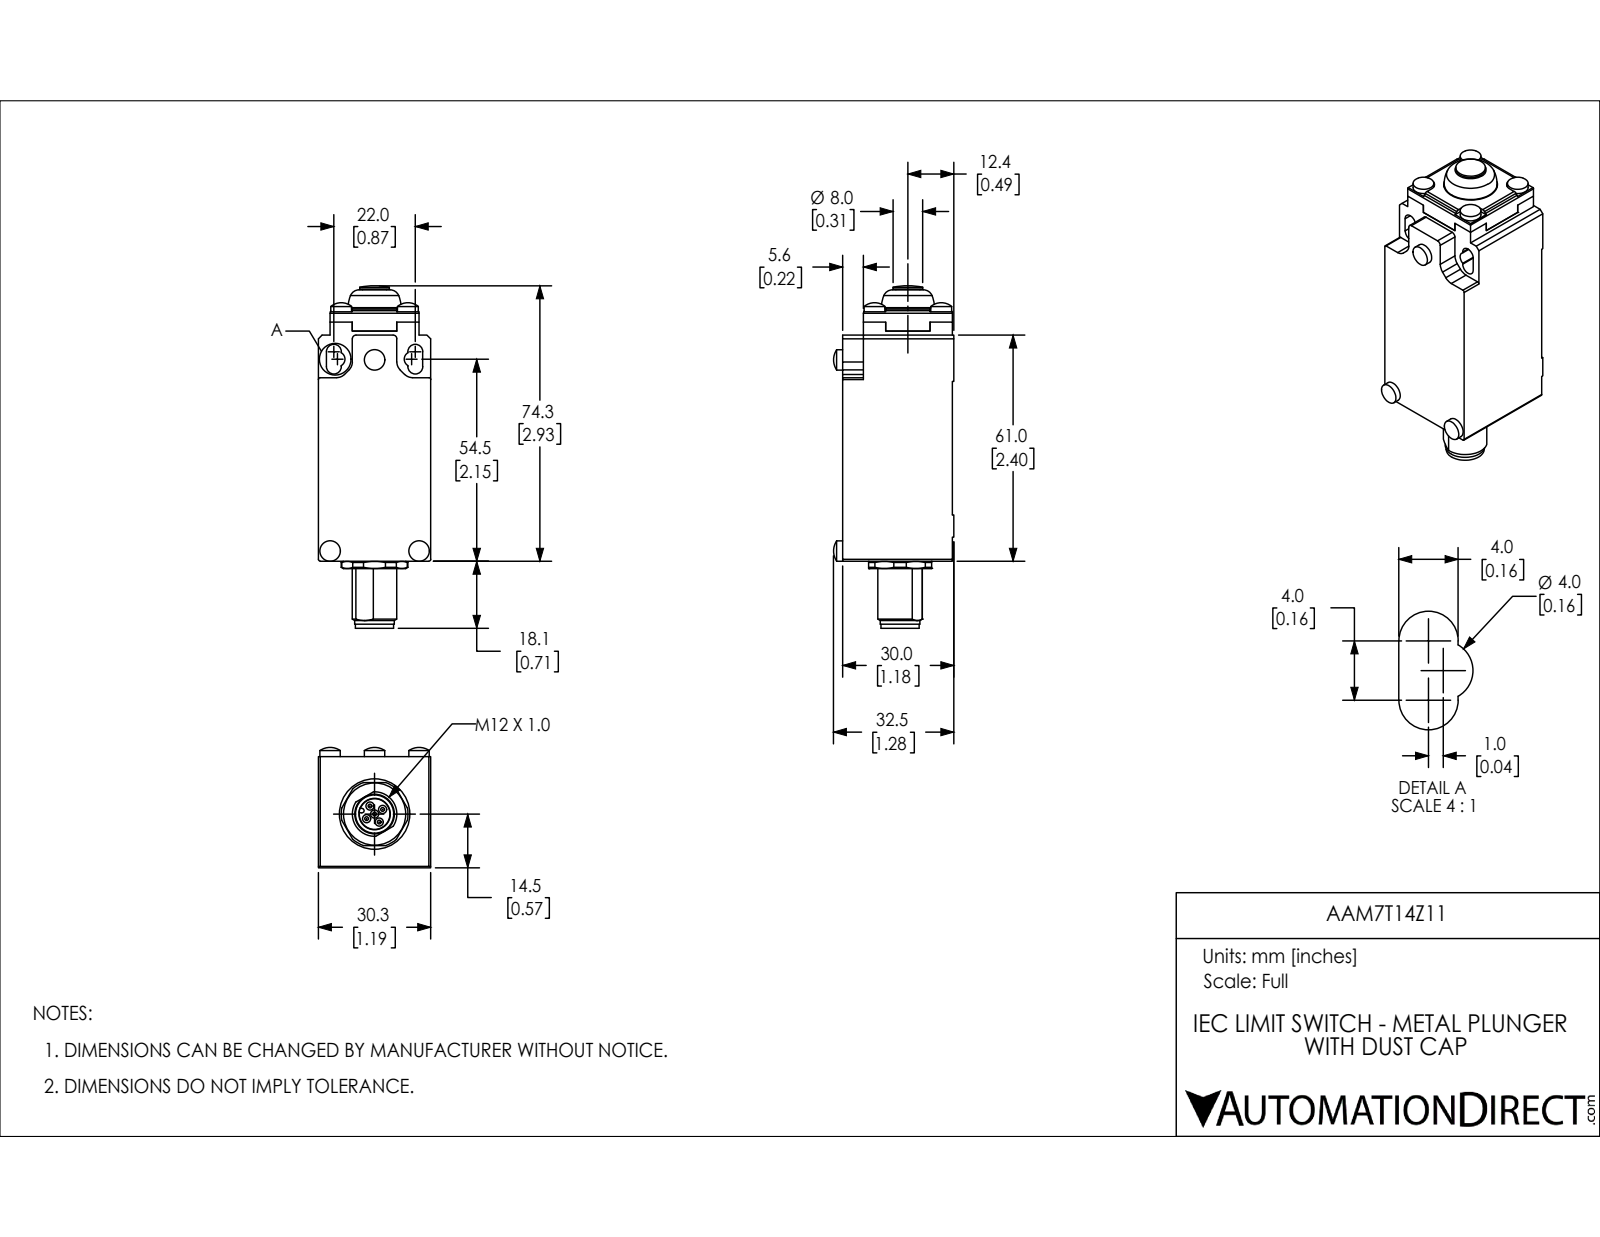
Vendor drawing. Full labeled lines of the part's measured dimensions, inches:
Part name (STEP PRODUCT): AAM7T14Z11
STEP written by: SolidWorks 2018 (AUTOMOTIVE_DESIGN)
Units: inches
Bodies: 5 solids, 303 faces (120 planar, 134 cylindrical, 49 other)
Overall size (bounding box): 3.638 × 1.28 × 1.193
Volume: 3.654 in³ · Surface area: 24.75 in²
Round holes (diameter × count): ⌀0.087 ×5, ⌀0.319 ×1, ⌀0.512 ×1, ⌀0.551 ×1, ⌀0.571 ×1, ⌀0.63 ×1
Round bosses / shafts (diameter × count): ⌀0.055 ×5, ⌀0.039 ×5, ⌀0.22 ×4, ⌀0.217 ×3, ⌀0.563 ×1, ⌀0.421 ×1, ⌀0.406 ×1, ⌀0.315 ×1
Partial cylindrical surfaces — rounded edges, fillets, slot ends (radius × count): R0.039 ×10, R0.118 ×8, R0.079 ×6, R0.02 ×4, R0.024 ×1, R0.236 ×1, R0.354 ×1, R0.394 ×1
Main face-to-face distances: 1.193, 1.165, 0.016, 1.181, 0.236, 2.444, 0.945, 0.043, 2.445, 0.244
Hole centre spacings: 0.098, 0.139, 0.197, 0.044, 0.083, 0.096, 0.154, 0.176
